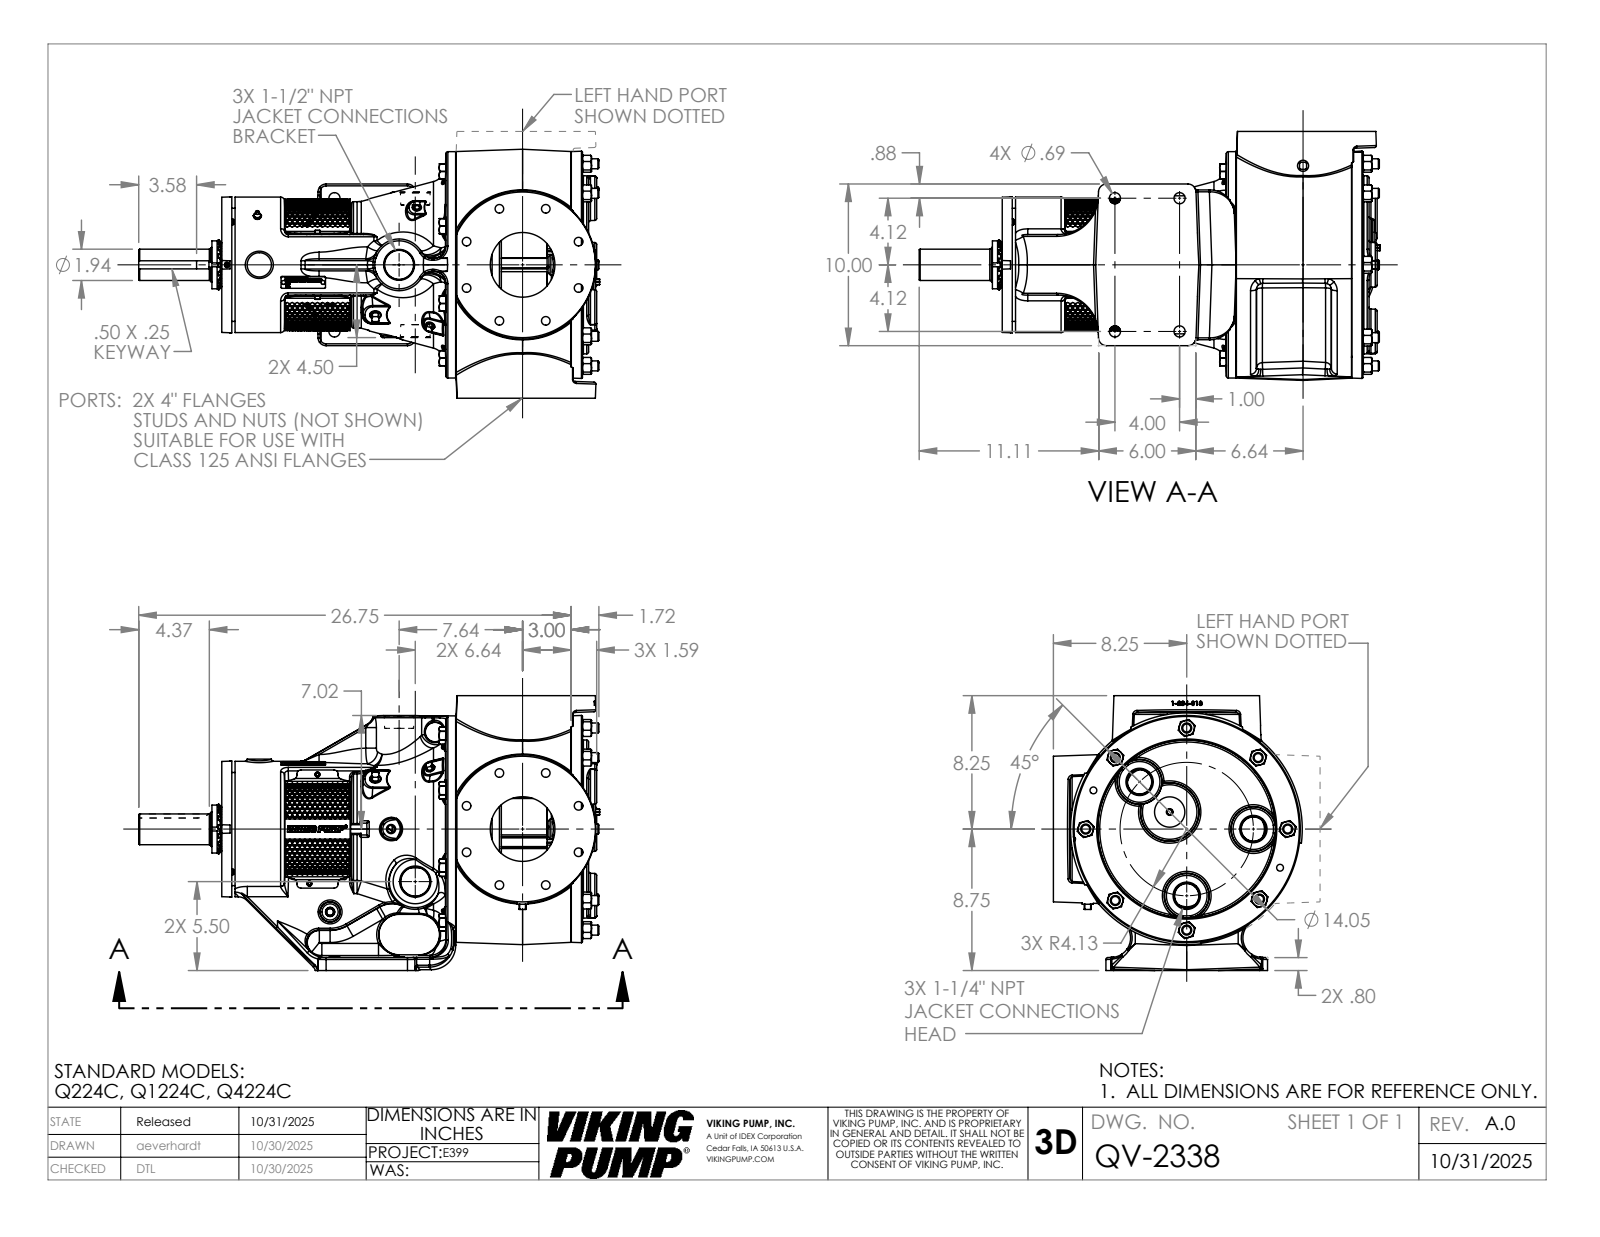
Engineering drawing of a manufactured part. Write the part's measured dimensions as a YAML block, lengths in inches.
part_name: "QV-2338"
step_written_by: "SolidWorks 2024 (AUTOMOTIVE_DESIGN)"
units: inches
bodies: {solids: 1, faces: 3857, planar: 1305, cylindrical: 587, other: 1965}
overall_size: [28.514, 19.12, 17.519]
volume: 2352
surface_area: 2034
round_holes:
  - {diameter: 0.266, count: 8}
  - {diameter: 1.157, count: 8}
  - {diameter: 0.25, count: 6}
  - {diameter: 0.531, count: 4}
  - {diameter: 0.688, count: 4}
  - {diameter: 0.159, count: 2}
  - {diameter: 0.313, count: 2}
  - {diameter: 0.422, count: 2}
  - {diameter: 0.453, count: 1}
  - {diameter: 2.157, count: 1}
  - {diameter: 2.167, count: 1}
  - {diameter: 2.182, count: 1}
round_bosses_or_shafts:
  - {diameter: 0.617, count: 24}
  - {diameter: 0.625, count: 16}
  - {diameter: 0.437, count: 3}
  - {diameter: 0.312, count: 3}
  - {diameter: 0.375, count: 2}
  - {diameter: 14, count: 1}
  - {diameter: 8.38, count: 1}
  - {diameter: 6.997, count: 1}
partial_cylinders:
  - {radius: 0.12, count: 56}
  - {radius: 0.75, count: 22}
  - {radius: 0.015, count: 18}
  - {radius: 0.092, count: 18}
  - {radius: 0.07, count: 16}
  - {radius: 0.5, count: 12}
  - {radius: 0.25, count: 10}
  - {radius: 0.06, count: 8}
face_to_face_distances: [0.38, 17, 22.317, 22.697, 1.25, 3.82, 18.498, 18.878, 7.972, 4.153]
hole_center_spacings: [3.75, 2.079, 5.783, 2.713, 3.133, 3.788, 5.423, 5.932]
